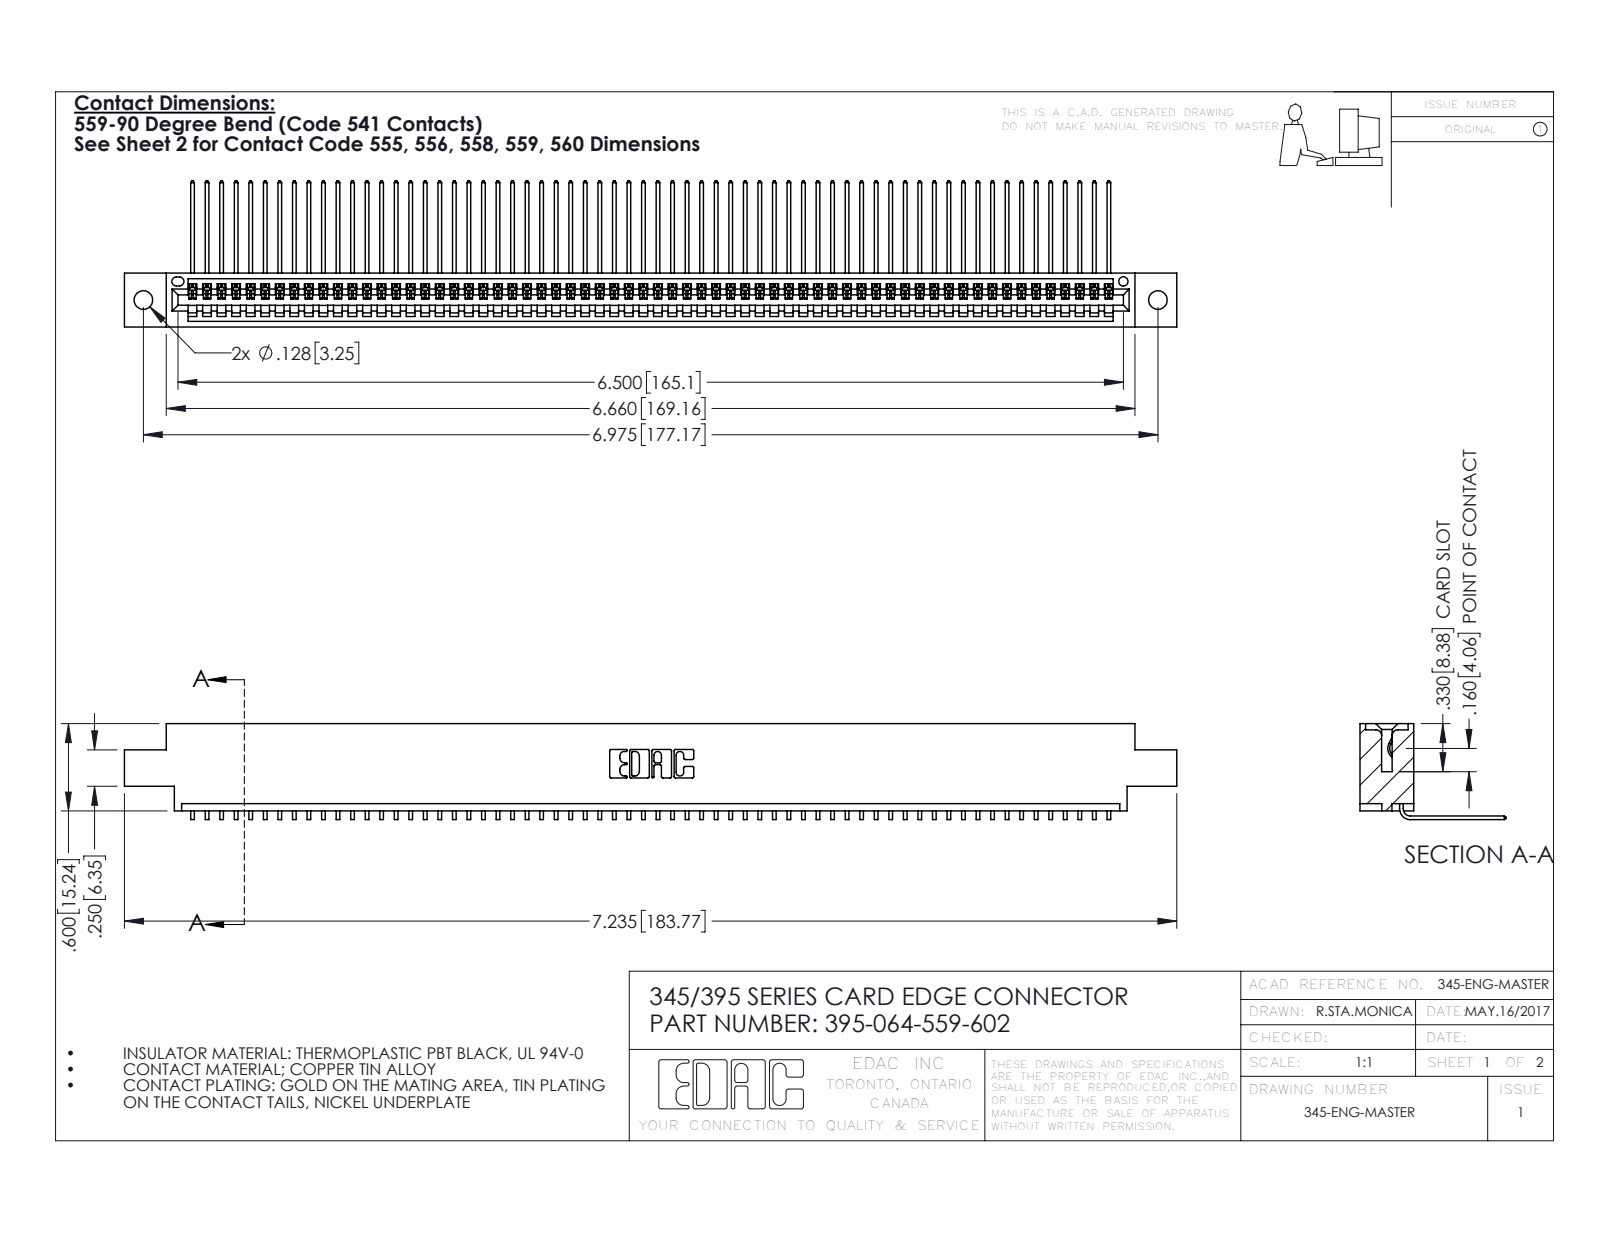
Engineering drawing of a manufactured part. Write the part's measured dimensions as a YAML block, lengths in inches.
part_name: "395-064-559-602; 345 Part_0.170 Offset - 0.128 Dia; 345-292-001_558 559 Tail - 1"
step_written_by: "SolidWorks 2016 (CONFIG_CONTROL_DESIGN)"
units: inches
bodies: {solids: 65, faces: 3970, planar: 2772, cylindrical: 1198, other: 0}
overall_size: [7.235, 1.005, 0.659]
volume: 1.08
surface_area: 38.64
round_holes:
  - {diameter: 0.128, count: 2}
  - {diameter: 0.064, count: 1}
partial_cylinders:
  - {radius: 0.006, count: 128}
  - {radius: 0.01, count: 22}
  - {radius: 0.007, count: 6}
  - {radius: 0.031, count: 6}
  - {radius: 0.026, count: 3}
  - {radius: 0.031, count: 2}
  - {radius: 0.04, count: 2}
  - {radius: 0.014, count: 1}
face_to_face_distances: [0.072, 0.298, 0.37, 0.2, 0.098, 0.272, 0.025, 0.225, 0.175, 0.149]
hole_center_spacings: [0.27, 6.739, 6.975]
